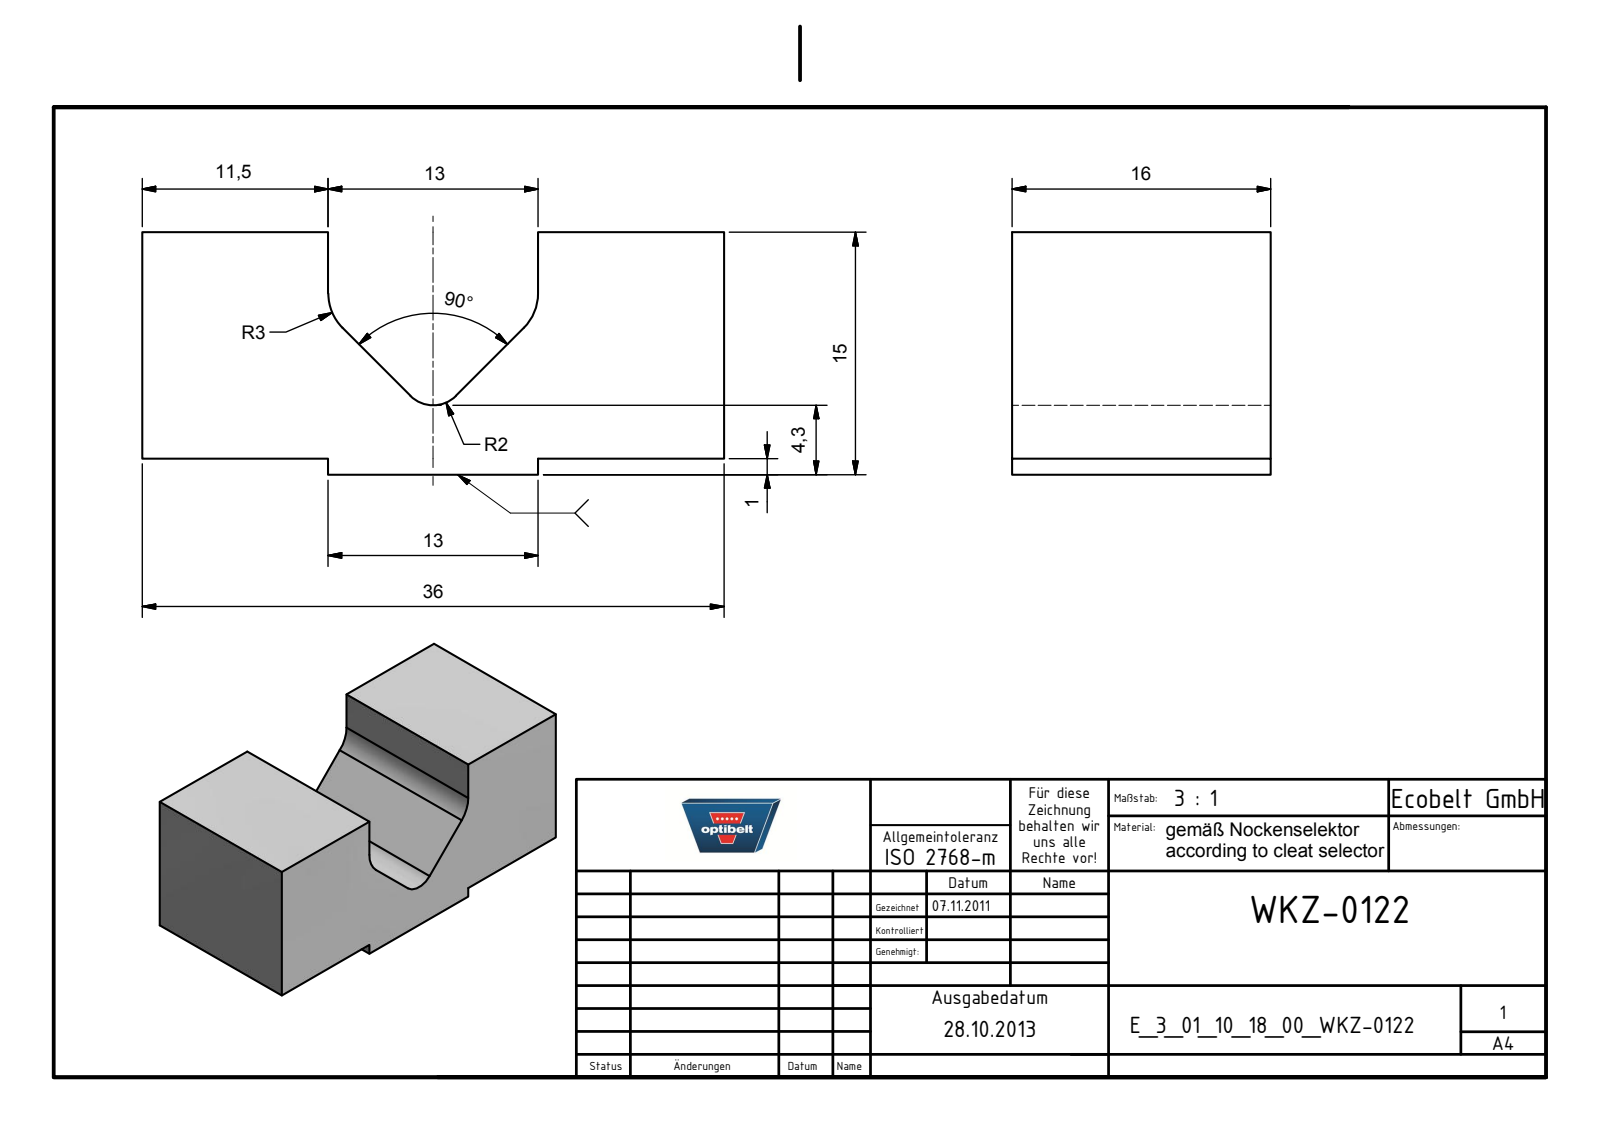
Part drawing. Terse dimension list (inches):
name: E_3_01_10_18_00_WKZ-0122
written by: Autodesk Inventor 2025 (AUTOMOTIVE_DESIGN)
unit: in
bodies: 1 solid, 18 faces (15 planar, 3 cylindrical, 0 other)
size: 1.417 × 0.63 × 0.591
volume: 0.401 in³; area: 4.157 in²
rounds: 2× R0.118, 1× R0.079
face distances: 0.63, 0.551, 1.417, 0.039, 0.591, 0.453, 0.965, 0.512
